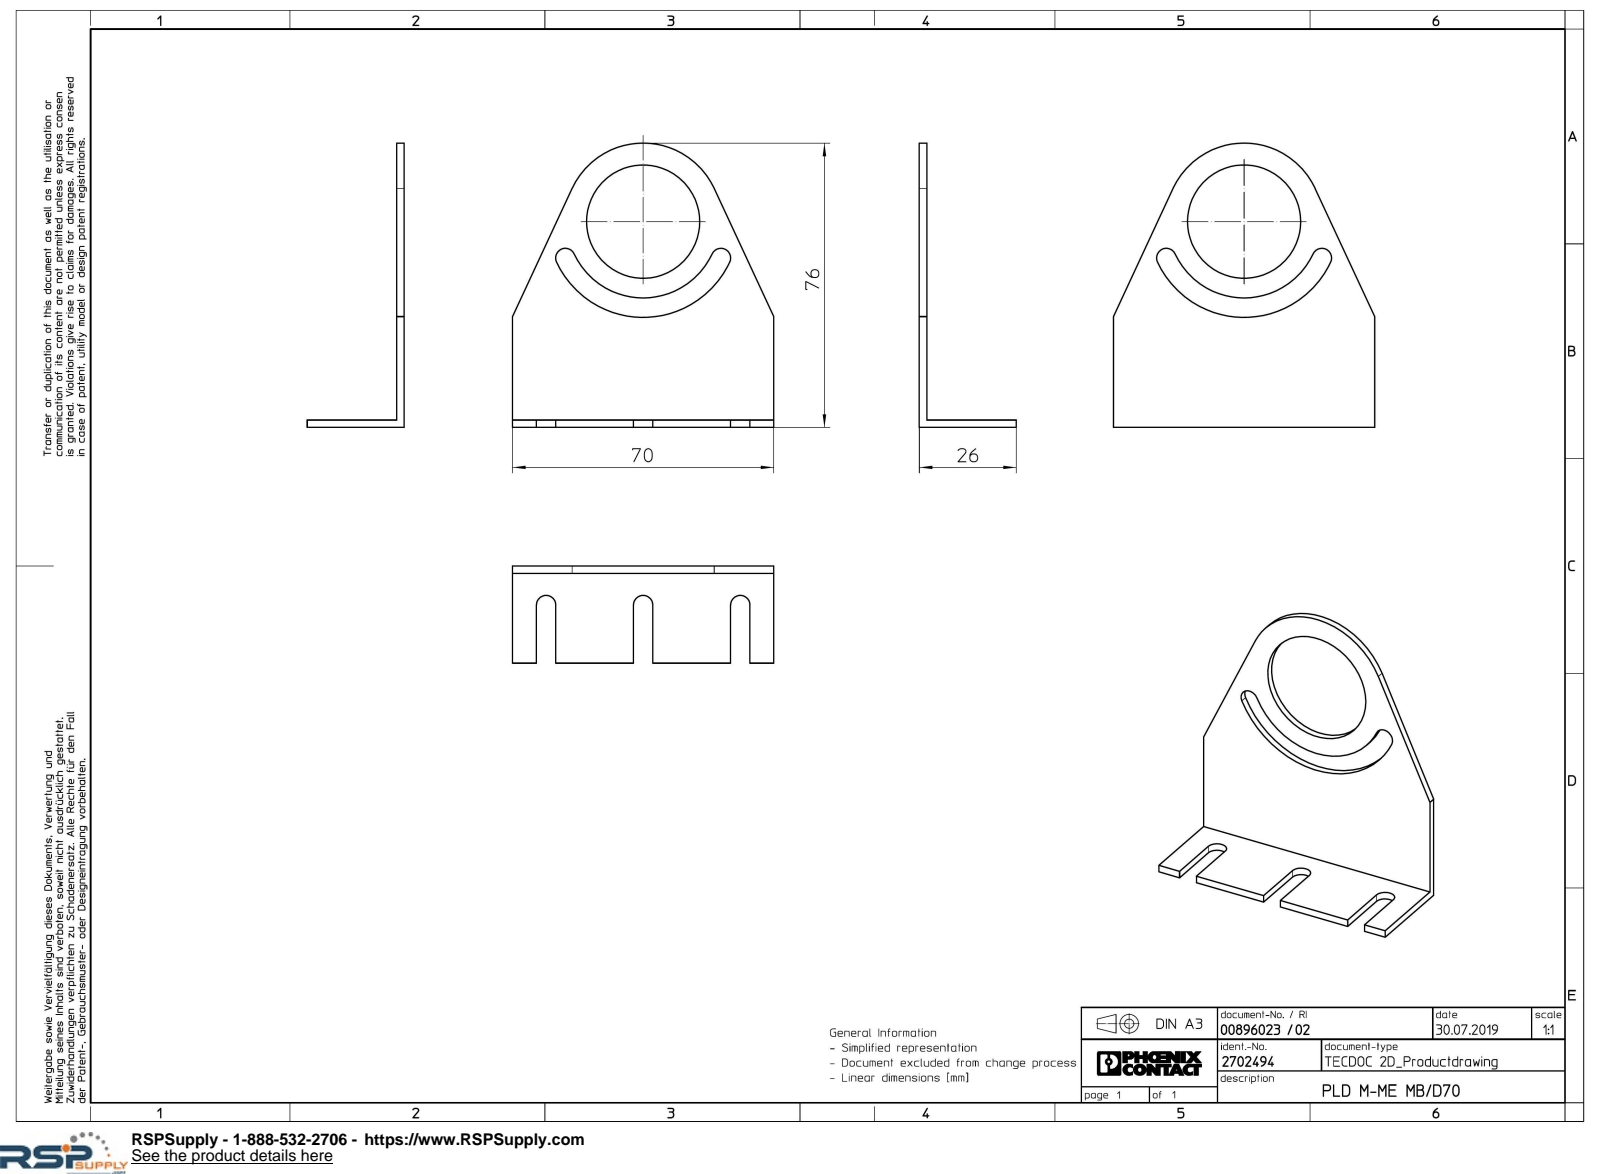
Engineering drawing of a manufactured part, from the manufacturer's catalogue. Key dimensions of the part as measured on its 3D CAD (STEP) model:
Part name (STEP PRODUCT): PLD_M_ME_MB_D70-select
STEP written by: Creo Elements/Direct Modeling 20.1A 29-Sep-2018 (C) Parametric Technology GmbH (AUTOMOTIVE_DESIGN)
Units: millimetres
Bodies: 1 solid, 28 faces (18 planar, 10 cylindrical, 0 other)
Overall size (bounding box): 76 × 70 × 26
Volume: 9 297 mm³ · Surface area: 10 534 mm²
Round holes (diameter × count): ⌀30.3 ×1
Partial cylindrical surfaces — rounded edges, fillets, slot ends (radius × count): R2.6 ×5, R20.4 ×1, R21 ×1, R25.6 ×1
Main face-to-face distances: 2, 26, 24, 70, 5.2, 6.4, 11.6, 32.4, 37.6, 58.4
